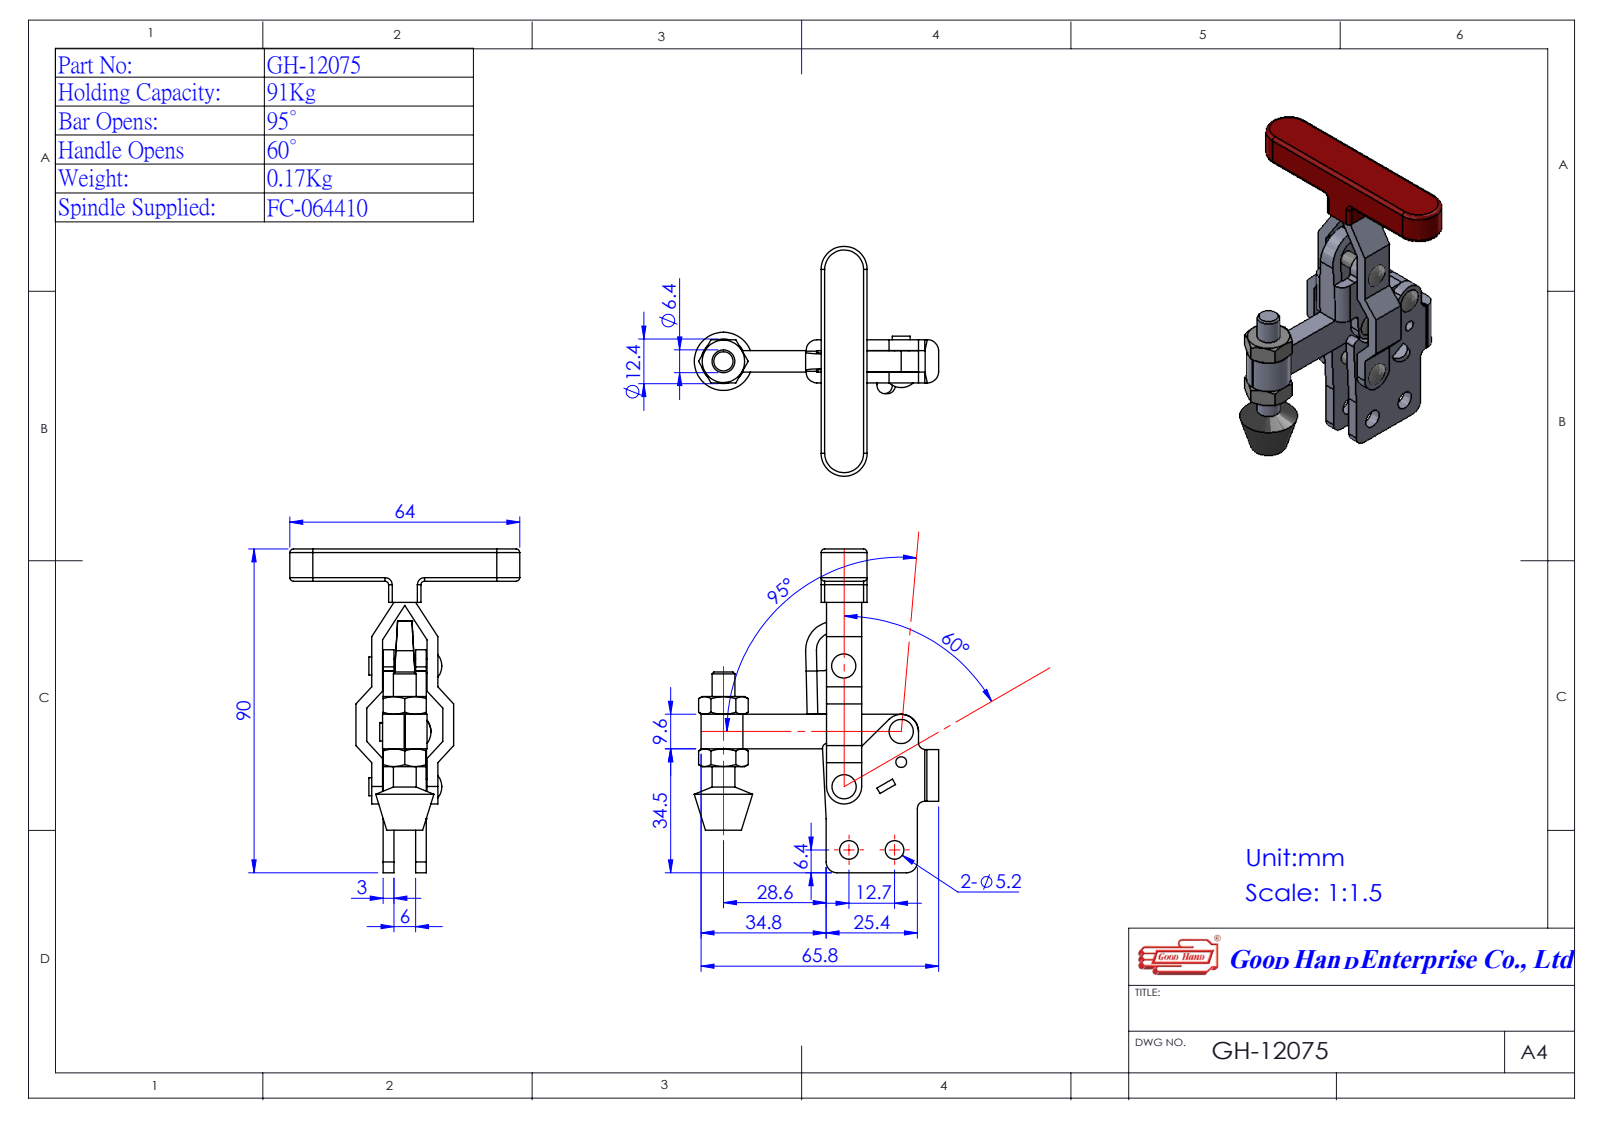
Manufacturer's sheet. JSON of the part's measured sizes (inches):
{"part_name": "Group1^GH-12075(簡化); 11205008-1^GH-12075(簡化); Group3^GH-12075(簡化); GH-12075(簡化) (+2 more)", "step_written_by": "SolidWorks 2016 (AUTOMOTIVE_DESIGN)", "units": "inches", "bodies": {"solids": 6, "faces": 234, "planar": 107, "cylindrical": 103, "other": 24}, "overall_size": [3.546, 2.67, 2.52], "volume_in3": 1.647, "surface_area_in2": 28.19, "round_holes": [[0.118, 5], [0.205, 2], [0.252, 1]], "round_bosses_or_shafts": [[0.197, 4], [0.488, 1], [0.25, 1], [0.118, 1]], "partial_cylinders_radius": [[0.079, 4], [0.122, 4], [0.004, 2], [0.039, 2], [0.118, 2], [0.177, 2], [0.197, 2], [0.252, 2]], "face_to_face_distances": [0.118, 0.354, 0.236, 0.472, 0.126, 0.48, 0.347, 0.504, 0.362, 0.173], "hole_center_spacings": [0.335, 0.5, 0.597, 0.614, 0.685, 0.698, 0.698, 0.724]}
